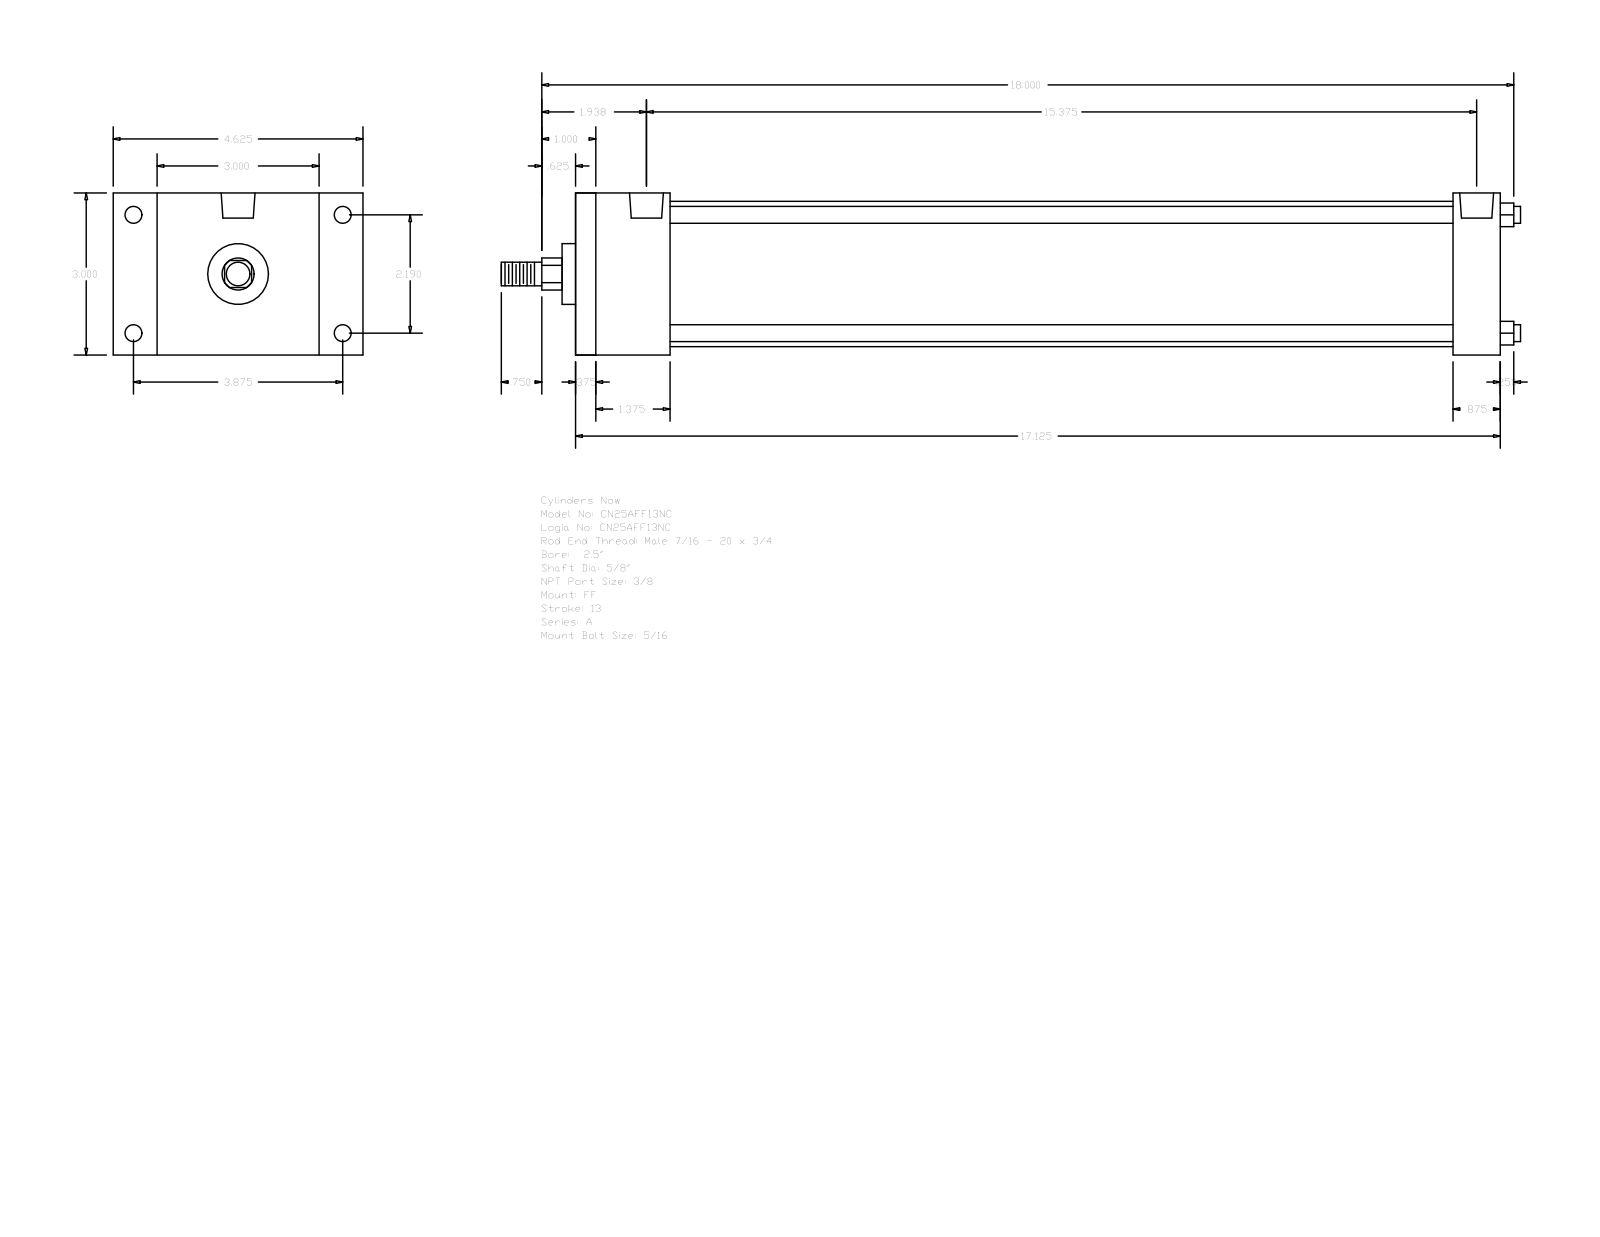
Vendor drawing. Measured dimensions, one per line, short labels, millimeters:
name: A_FF__0250_0.625
written by: GSSL Pune (CONFIG_CONTROL_DESIGN)
unit: mm
bodies: 0 solids, 92 faces (64 planar, 28 cylindrical, 0 other)
size: 479.43 × 117.47 × 76.2
holes: 4× ⌀5.56, 4× ⌀7.94, 2× ⌀15.93
bosses: 4× ⌀7.94, 1× ⌀68.33, 1× ⌀28.57, 1× ⌀15.88, 1× ⌀11.11
rounds: 1× R7.54
face distances: 76.2, 434.97, 9.52, 425.45, 44.45, 34.93, 412.74, 403.22, 368.29, 390.52
hole spacings: 2.38, 55.62, 98.42, 113.05, 392.91, 395.29, 390.53
